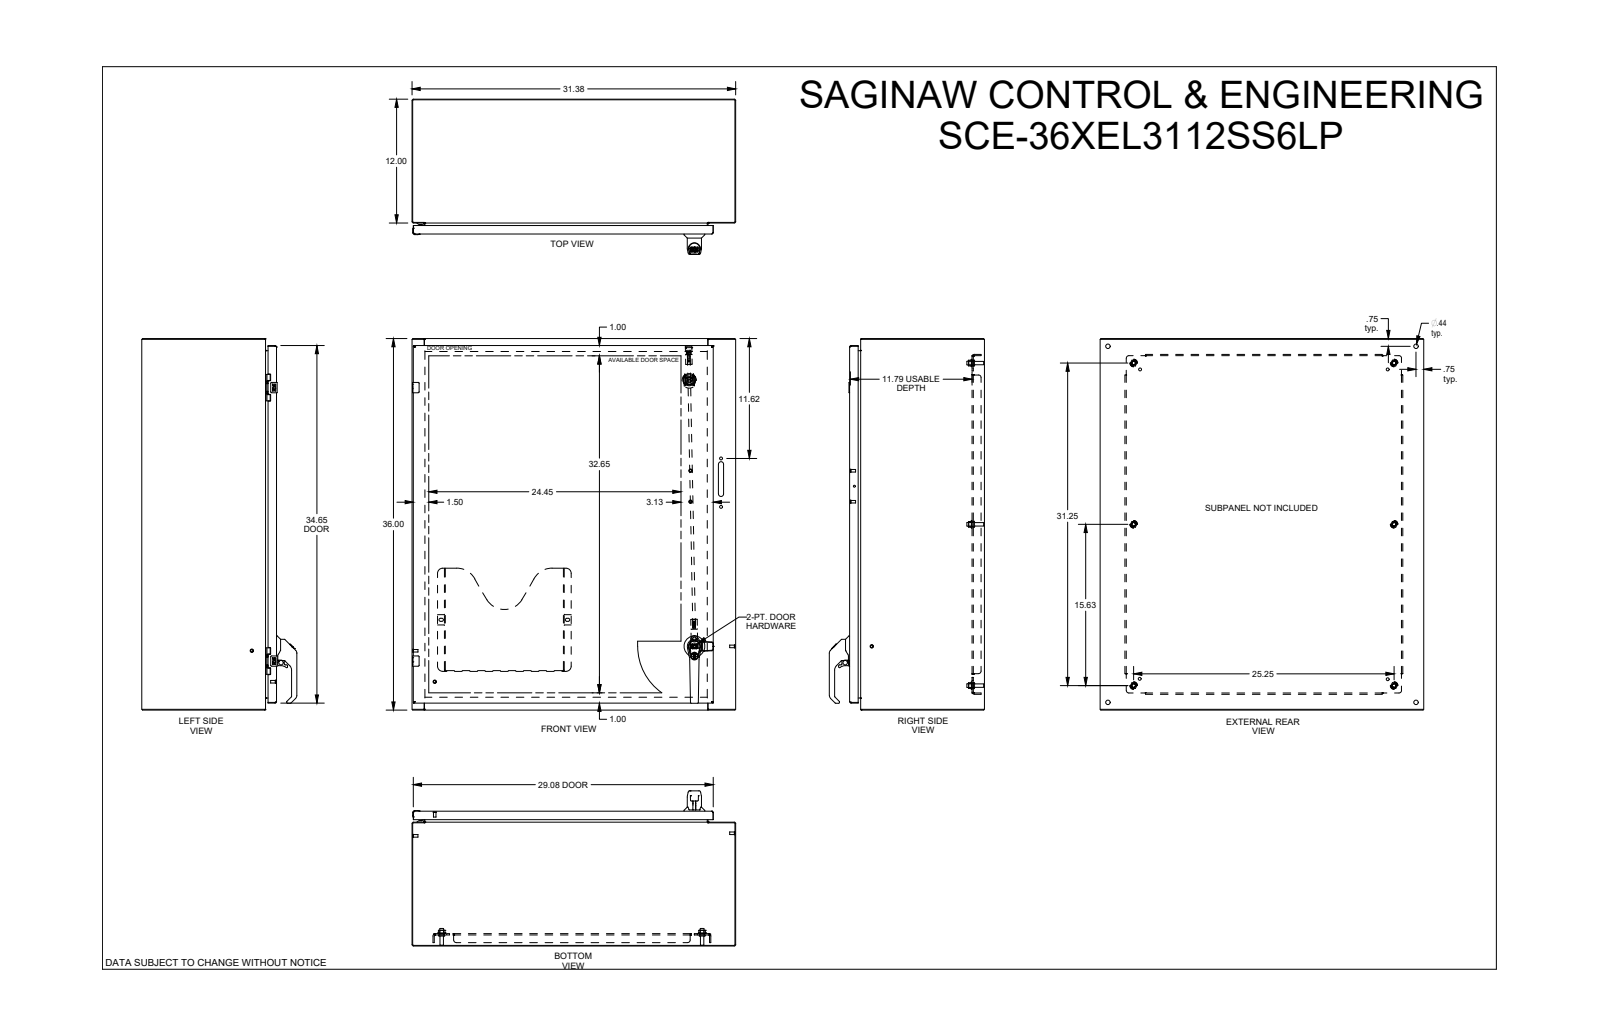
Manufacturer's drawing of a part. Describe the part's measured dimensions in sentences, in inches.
The part is named "SCE-36XEL3112SS6LP". Its 3-D file was written by "SolidWorks 2019 (CONFIG_CONTROL_DESIGN)". It is 71 solids with 4738 faces: 1767 planar, 1238 cylindrical and 1733 other. Overall it measures 36 by 31.375 by 15.036 inches. Its volume is 473.4 cubic inches and its surface area 10 907 square inches. Round holes: 6 of diameter 0.281, 6 of diameter 0.367, 6 of diameter 0.5, 5 of diameter 0.266, 4 of diameter 0.172, 4 of diameter 0.205, 4 of diameter 0.244, 4 of diameter 0.375, 4 of diameter 0.437, 3 of diameter 0.25, 3 of diameter 0.25, 2 of diameter 0.138. Round bosses or shafts: 8 of diameter 0.248, 6 of diameter 0.366, 6 of diameter 0.332, 6 of diameter 0.17, 4 of diameter 0.25, 3 of diameter 0.563, 3 of diameter 0.196, 2 of diameter 0.341. Partial cylindrical surfaces (rounded edges, fillets, slot ends): 69 of radius 0.03, 54 of radius 0.015, 48 of radius 0.01, 36 of radius 0.02, 34 of radius 0.02, 31 of radius 0.04, 30 of radius 0.039, 26 of radius 0.005. The main face-to-face distances are 0.075, 12.993, 0.075, 12.918, 13.068, 1.125, 1.2, 11.868, 11.793, 0.125. The hole center spacings are 26.5, 0.985, 0.02, 4.493, 26.542, 26.562, 0.472, 0.725.
